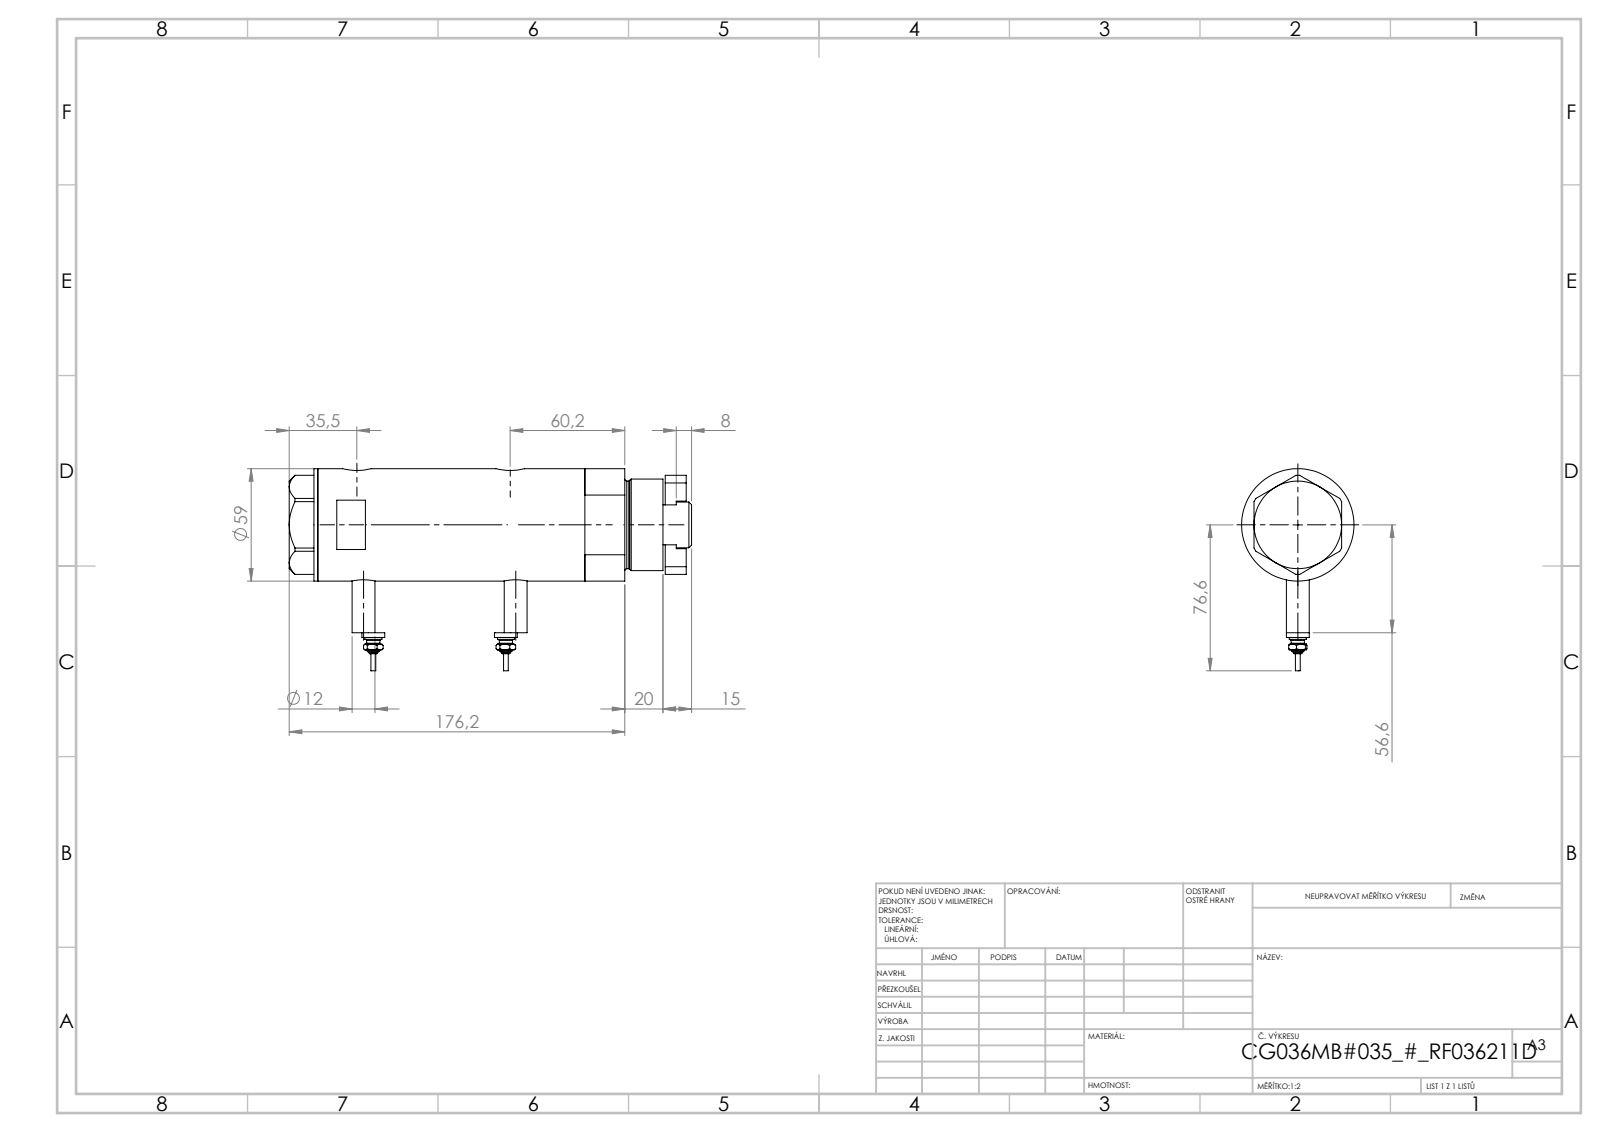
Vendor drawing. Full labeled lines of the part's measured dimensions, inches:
Part name (STEP PRODUCT): V270CG_VC; V270CG_MIDDLE; V270CG_FRONT; V270CG_RF211D (+2 more)
STEP written by: SolidWorks 2019 (CONFIG_CONTROL_DESIGN)
Units: inches
Bodies: 8 solids, 272 faces (105 planar, 93 cylindrical, 74 other)
Overall size (bounding box): 7.812 × 3.594 × 2.323
Volume: 27.86 in³ · Surface area: 156.9 in²
Round holes (diameter × count): ⌀0.24 ×4, ⌀0.413 ×4, ⌀0.197 ×2, ⌀0.383 ×2, ⌀0.492 ×2, ⌀0.591 ×2, ⌀0.335 ×1, ⌀0.984 ×1, ⌀1.043 ×1, ⌀1.417 ×1, ⌀1.575 ×1, ⌀2.047 ×1
Round bosses / shafts (diameter × count): ⌀0.472 ×3, ⌀0.354 ×2, ⌀0.276 ×2, ⌀0.171 ×2, ⌀0.094 ×2, ⌀2.323 ×1, ⌀1.89 ×1, ⌀1.811 ×1
Main face-to-face distances: 3.635, 0.925, 2.71, 0.591, 1.516, 4.226, 1.496, 7.221, 0.079, 6.631
Hole centre spacings: 0.784, 0.114, 0.138, 0.472, 1.495, 1.568, 2.644, 2.758
